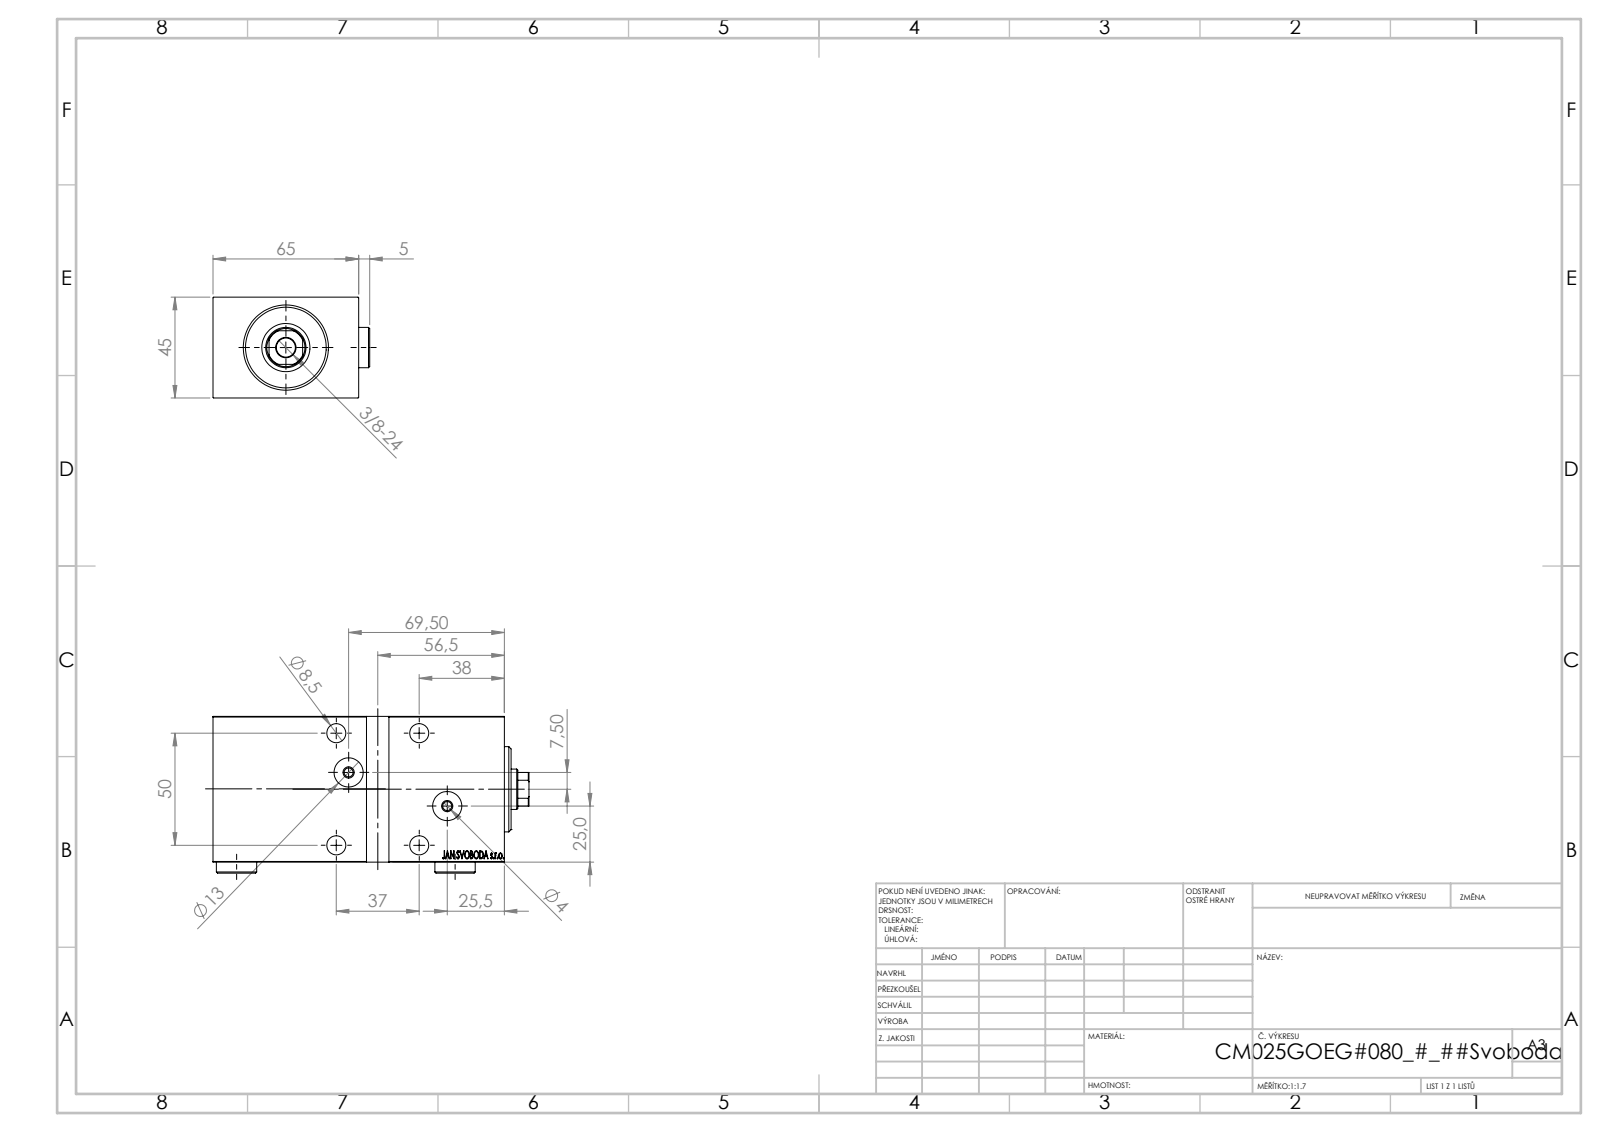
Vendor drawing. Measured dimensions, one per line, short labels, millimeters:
name: V450CM_G_VCP; V450CM_VC_G; V450CM_G_Body; Zatka_OIL_PORT
written by: SolidWorks 2019 (CONFIG_CONTROL_DESIGN)
unit: mm
bodies: 5 solids, 899 faces (443 planar, 58 cylindrical, 398 other)
size: 141 × 69.9 × 45
volume: 351 840 mm³; area: 65 110 mm²
holes: 5× ⌀8.5, 4× ⌀13.5, 2× ⌀4, 2× ⌀13, 1× ⌀18, 1× ⌀21.5, 1× ⌀25, 1× ⌀27, 1× ⌀35
bosses: 2× ⌀18, 2× ⌀5, 1× ⌀38
rounds: 1× R8.5
face distances: 45, 65, 130, 6, 119, 5, 124, 8, 125, 3
hole spacings: 37, 50, 62.2, 18.34, 21.51, 32.96, 34.82, 36.03
